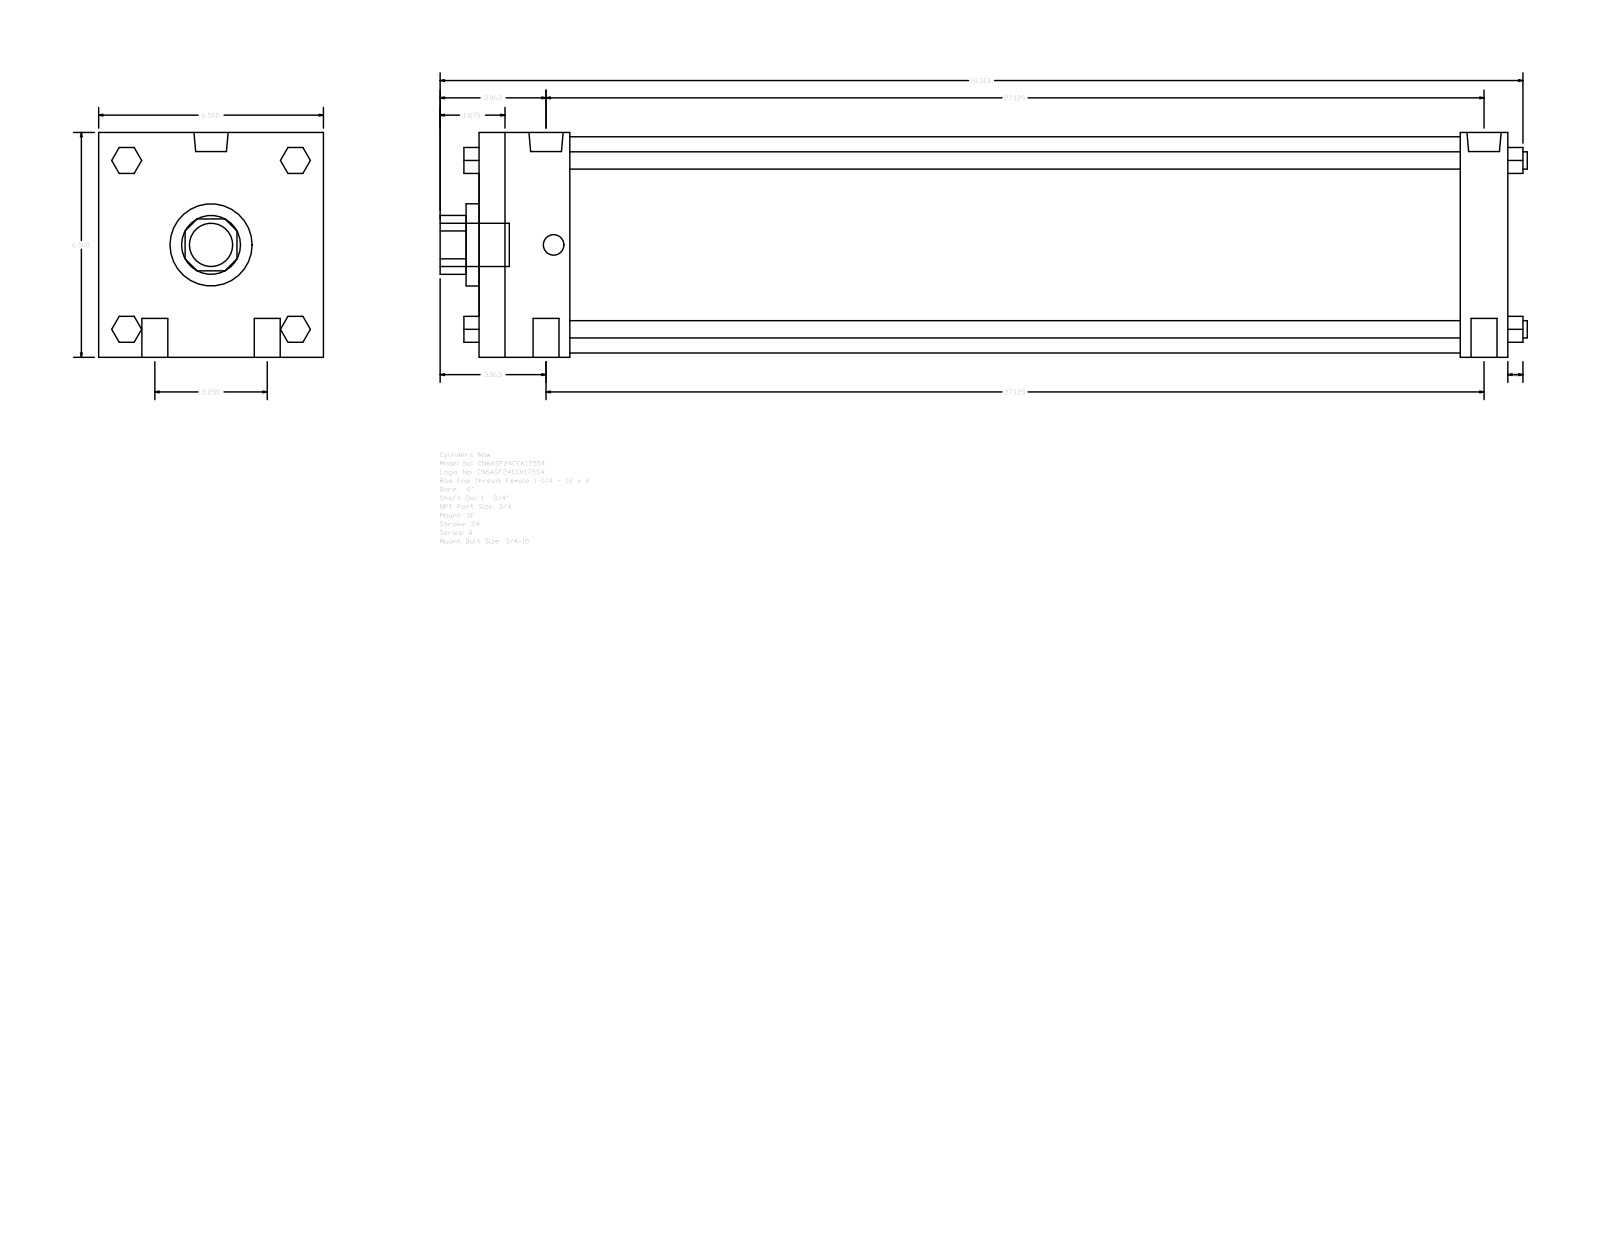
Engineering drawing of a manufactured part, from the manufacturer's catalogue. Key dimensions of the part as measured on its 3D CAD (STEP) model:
Part name (STEP PRODUCT): A_SF__0600_1.75
STEP written by: GSSL Pune (CONFIG_CONTROL_DESIGN)
Units: millimetres
Bodies: 0 solids, 124 faces (94 planar, 30 cylindrical, 0 other)
Overall size (bounding box): 798.51 × 165.1 × 165.1
Round holes (diameter × count): ⌀44.45 ×1, ⌀60.33 ×1, ⌀158.75 ×1
Round bosses / shafts (diameter × count): ⌀19.05 ×4, ⌀12.7 ×4, ⌀25.12 ×2, ⌀15.08 ×2, ⌀31.75 ×1
Partial cylindrical surfaces — rounded edges, fillets, slot ends (radius × count): R21.63 ×1
Main face-to-face distances: 165.1, 755.66, 720.73, 34.93, 66.68, 654.05, 688.98, 19.05, 61.97, 107.34
